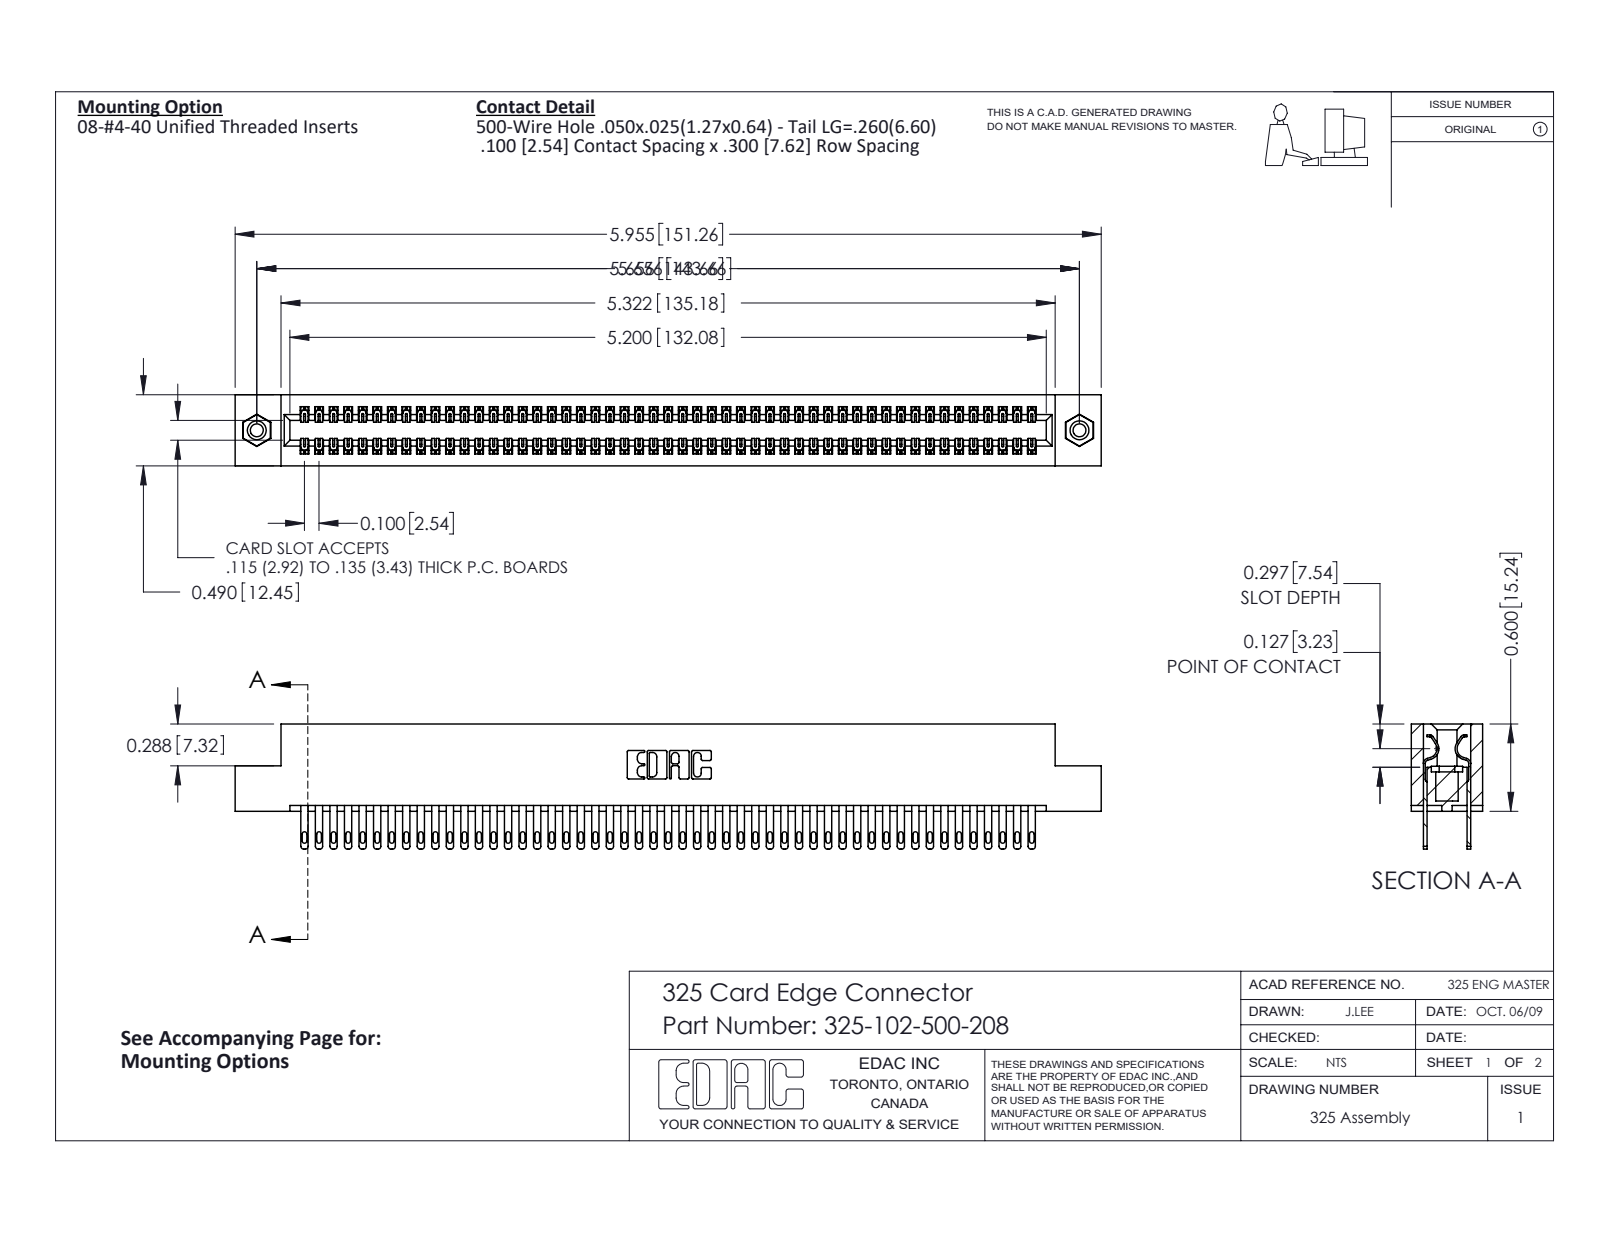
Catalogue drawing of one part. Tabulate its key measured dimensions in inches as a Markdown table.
| quantity | value |
| --- | --- |
| part name | 325 Part_TI; 345-250-001_345-250-003-102; 325-292-001_325-293-100; 325-102-500-208 |
| STEP written by | SolidWorks 2016 (CONFIG_CONTROL_DESIGN) |
| units | inches |
| bodies | 105 solids, 5070 faces (3162 planar, 1892 cylindrical, 16 other) |
| overall size | 5.955 × 0.86 × 0.49 |
| volume | 1.215 in³ |
| surface area | 39.36 in² |
| round holes (diameter × count) | 0.089 × 2, 0.125 × 2, 0.16 × 2 |
| round bosses / shafts (diameter × count) | 0.155 × 2 |
| partial cylindrical surfaces (radius × count) | 0.006 × 153, 0.016 × 102, 0.02 × 102, 0.01 × 22, 0.007 × 6, 0.031 × 6, 0.026 × 3, 0.014 × 2 |
| main face-to-face distances | 0.083, 0.407, 0.3, 0.107, 0.383, 0.025, 0.49, 0.325, 0.275, 0.56 |
| hole center spacings | 5.656 |
